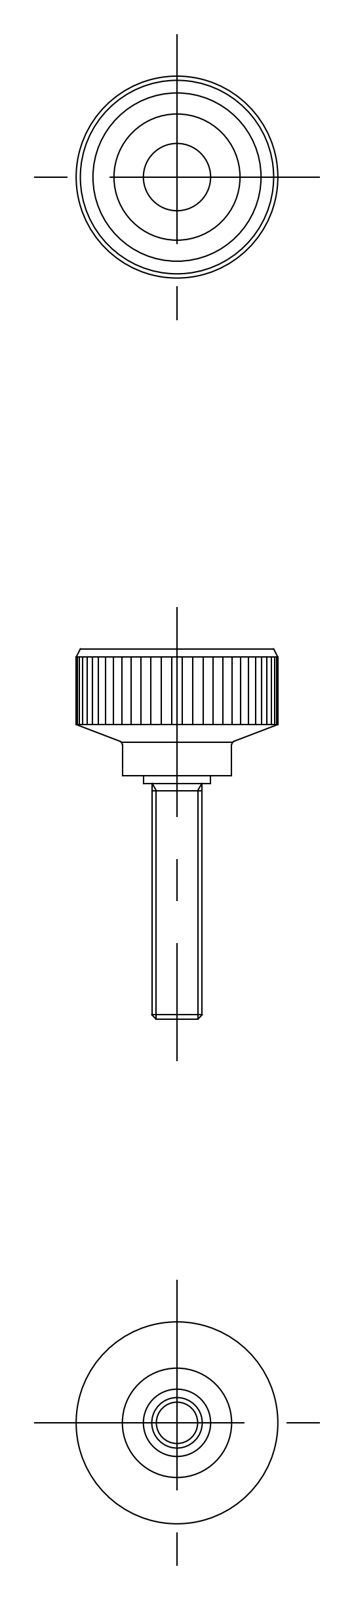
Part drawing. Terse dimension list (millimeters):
name: screw; knob; KKM_24_M6_28_5266_36
written by: CADfix (AUTOMOTIVE_DESIGN)
unit: mm
bodies: 2 solids, 35 faces (0 planar, 0 cylindrical, 35 other)
size: 44 × 24 × 24
volume: 4 464 mm³; area: 3 029 mm²
